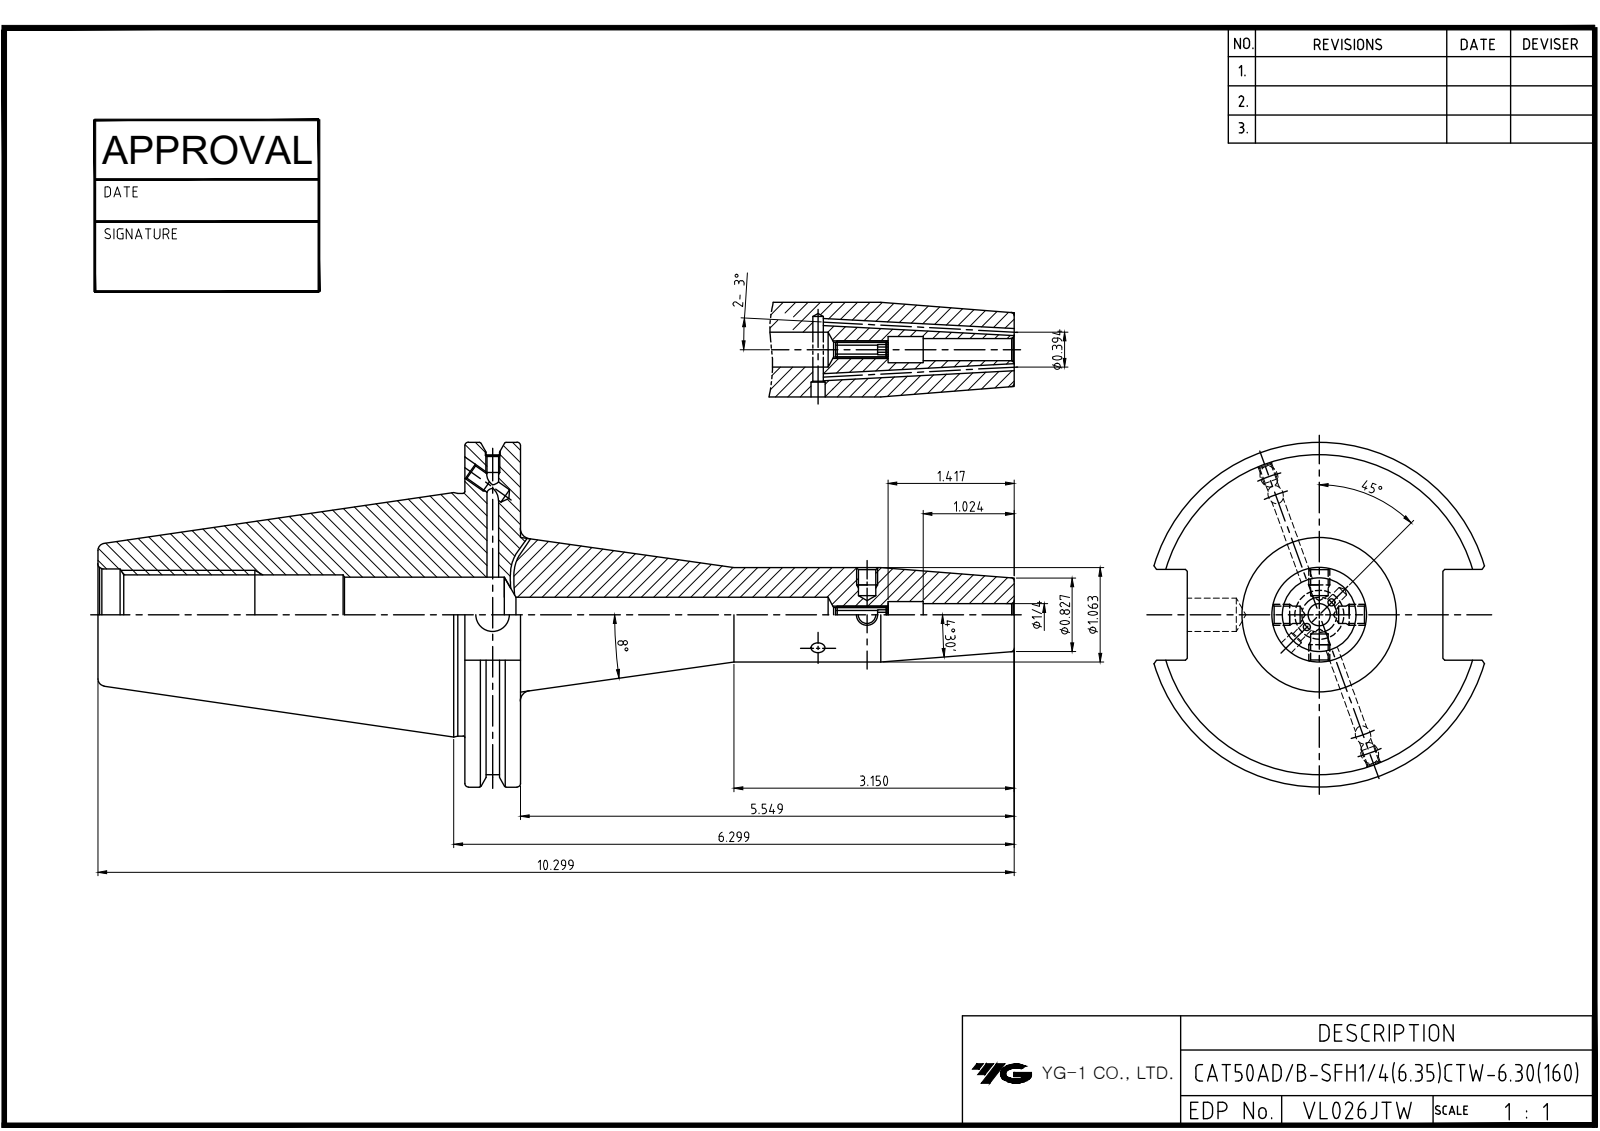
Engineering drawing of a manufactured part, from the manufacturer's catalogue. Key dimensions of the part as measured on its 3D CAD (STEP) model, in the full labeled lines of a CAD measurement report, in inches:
Part name (STEP PRODUCT): LO-CAT50ADB-SFH1_4CTW-6
STEP written by: Autodesk Inventor 2020 (AUTOMOTIVE_DESIGN)
Units: inches
Bodies: 1 solid, 89 faces (37 planar, 28 cylindrical, 24 other)
Overall size (bounding box): 10.299 × 3.875 × 3.728
Volume: 25.28 in³ · Surface area: 94.28 in²
Round holes (diameter × count): ⌀0.163 ×3, ⌀0.128 ×2, ⌀0.165 ×2, ⌀0.197 ×2, ⌀0.25 ×1, ⌀0.297 ×1, ⌀0.375 ×1, ⌀0.394 ×1, ⌀0.846 ×1, ⌀0.865 ×1, ⌀1.031 ×1
Round bosses / shafts (diameter × count): ⌀3.875 ×1, ⌀3.594 ×1, ⌀2.726 ×1, ⌀1.063 ×1
Main face-to-face distances: 0.625, 4.125, 4.75, 2.875, 1.02, 10.299, 6.174, 5.549, 4.363, 0.238
